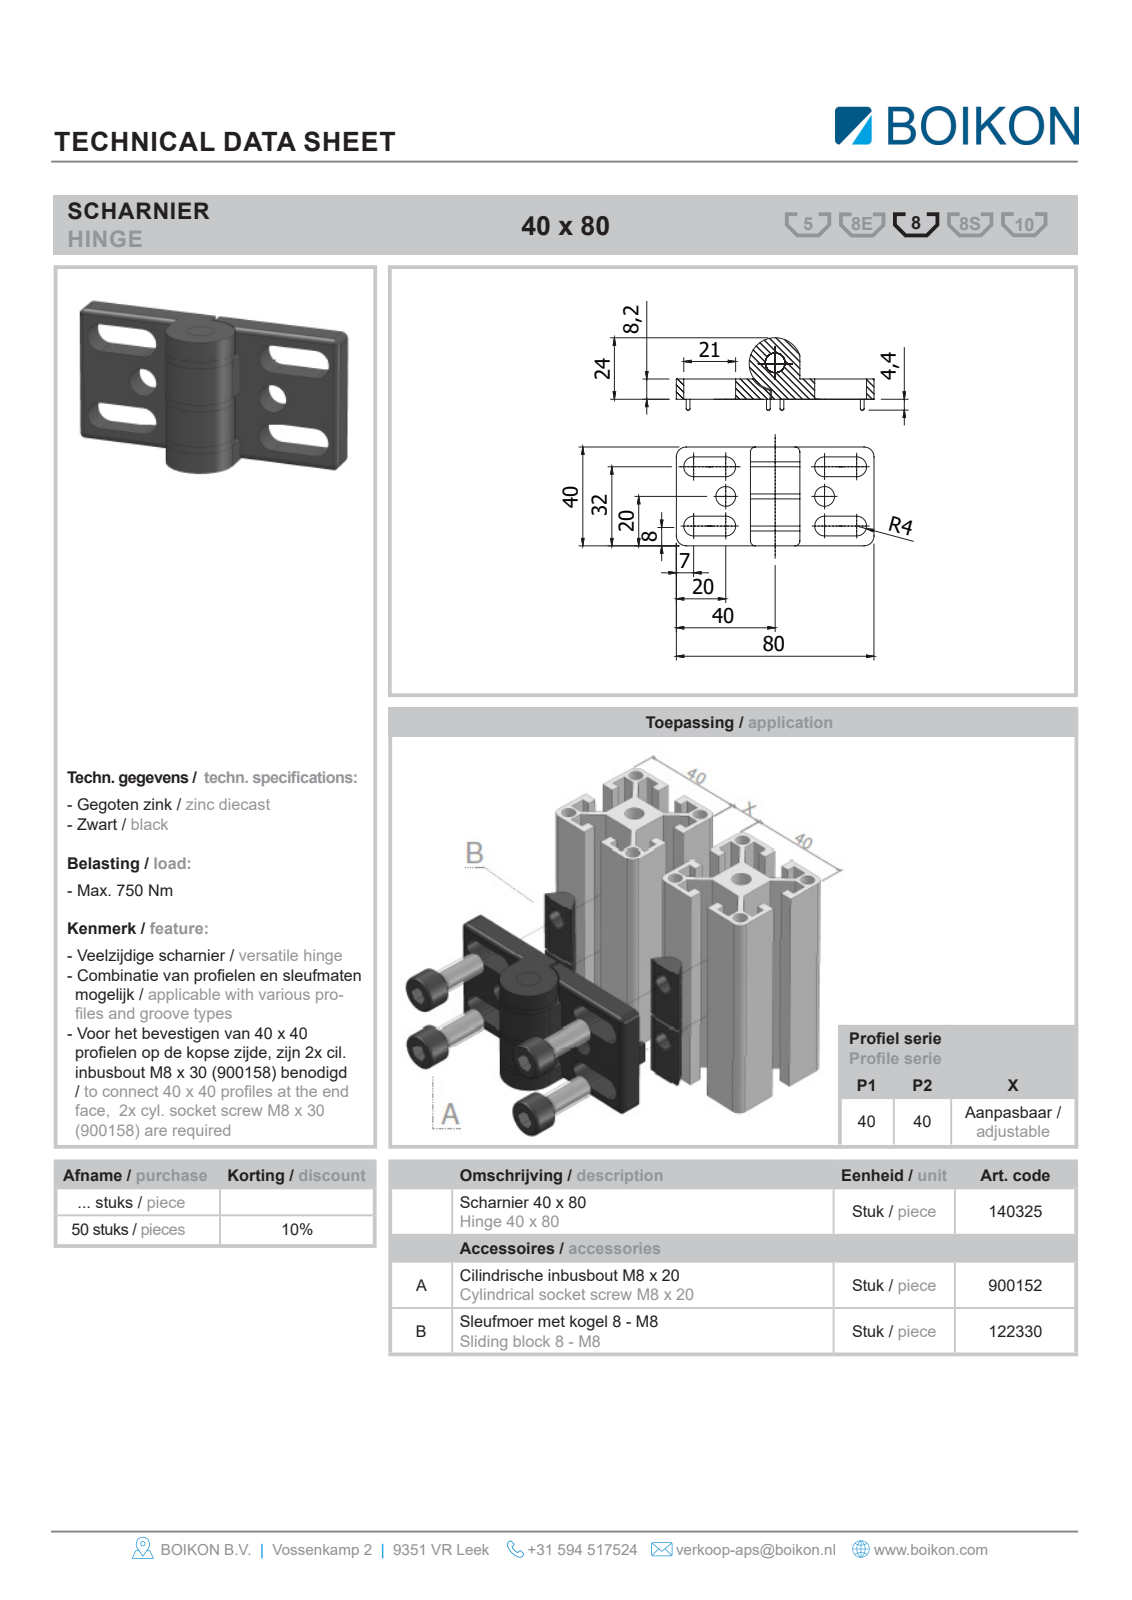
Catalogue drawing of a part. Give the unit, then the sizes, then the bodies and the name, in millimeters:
Units: millimetres
Overall size (bounding box): 80 × 40 × 28.5
Round holes (diameter × count): ⌀8.3 ×2, ⌀8 ×1
Round bosses / shafts (diameter × count): ⌀20 ×1
Partial cylindrical surfaces — rounded edges, fillets, slot ends (radius × count): R4.15 ×8, R1.5 ×4, R2 ×4, R10.5 ×1
Main face-to-face distances: 8, 13, 2, 34, 19, 21, 6, 32, 26, 15
Hole centre spacings: 40
Volume: 30 194 mm³ · Surface area: 16 992 mm²
Bodies: 6 solids, 105 faces (62 planar, 39 cylindrical, 4 other)
Part name (STEP PRODUCT): Root; 140325Scharnier 40x80BOIKON
STEP written by: HiCAD 2013 1802.4 Build 509 (AUTOMOTIVE_DESIGN)
